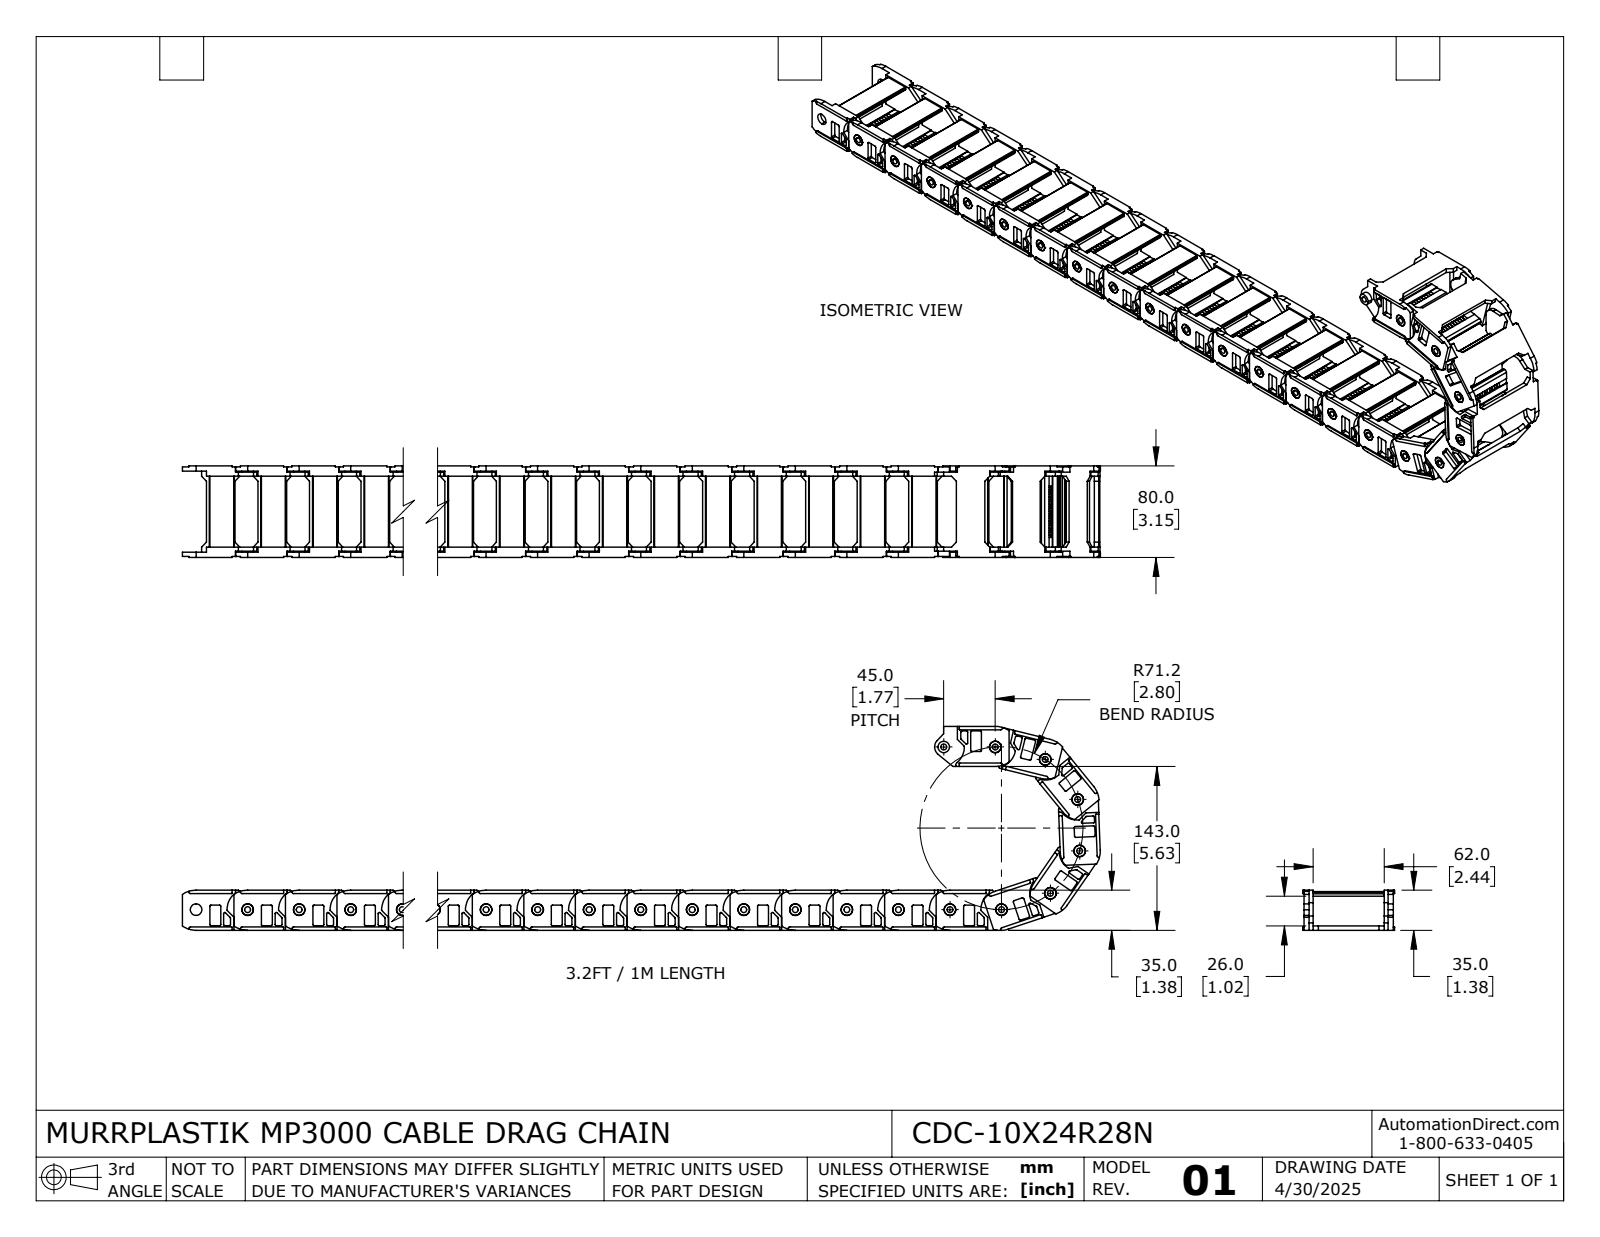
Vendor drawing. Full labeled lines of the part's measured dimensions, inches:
Part name (STEP PRODUCT): CDC-10X24R28N
STEP written by: SolidWorks 2024 (AUTOMOTIVE_DESIGN)
Units: inches
Bodies: 22 solids, 4400 faces (3300 planar, 1100 cylindrical, 0 other)
Overall size (bounding box): 32.216 × 7.013 × 3.15
Volume: 41.49 in³ · Surface area: 640.2 in²
Round holes (diameter × count): ⌀0.201 ×22, ⌀0.398 ×22
Round bosses / shafts (diameter × count): ⌀0.394 ×22
Partial cylindrical surfaces — rounded edges, fillets, slot ends (radius × count): R0.039 ×176, R0.02 ×88, R0.059 ×44, R0.079 ×44, R0.827 ×44, R0.11 ×22, R0.315 ×22, R0.709 ×22
Main face-to-face distances: 2.756, 0.315, 0.157, 0.146, 2.925, 0.169, 2.61, 2.441, 0.138, 0.15
Hole centre spacings: 1.772, 3.543, 5.315, 7.087, 8.858, 10.63, 12.402, 14.173
